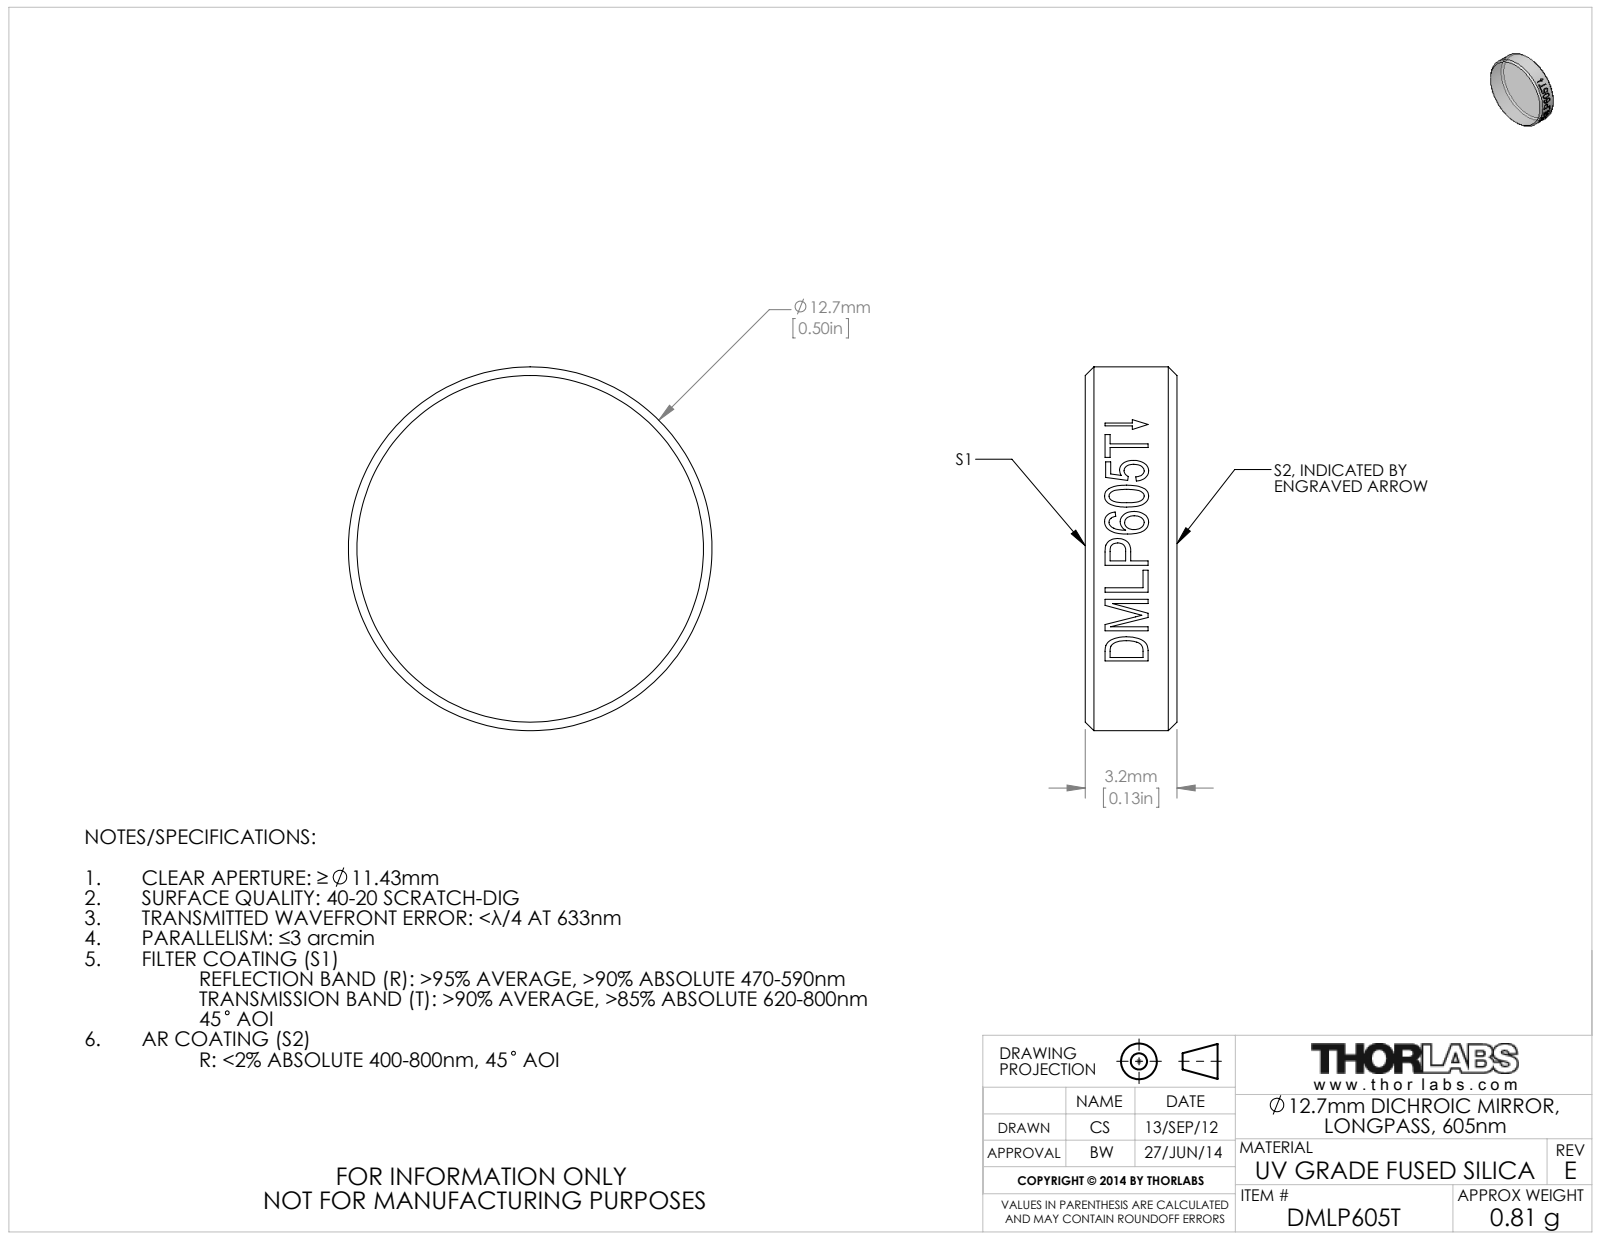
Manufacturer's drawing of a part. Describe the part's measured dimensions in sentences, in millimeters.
The part is named "24964-E0W". Its 3-D file was written by "SolidWorks 2011 (CONFIG_CONTROL_DESIGN)". It is 0 solids with 21 faces: 2 planar, 15 cylindrical and 4 other. Overall it measures 12.7 by 12.7 by 3.2 millimeters. Round bosses or shafts: 1 of diameter 12.7. The main face-to-face distances are 3.2.
